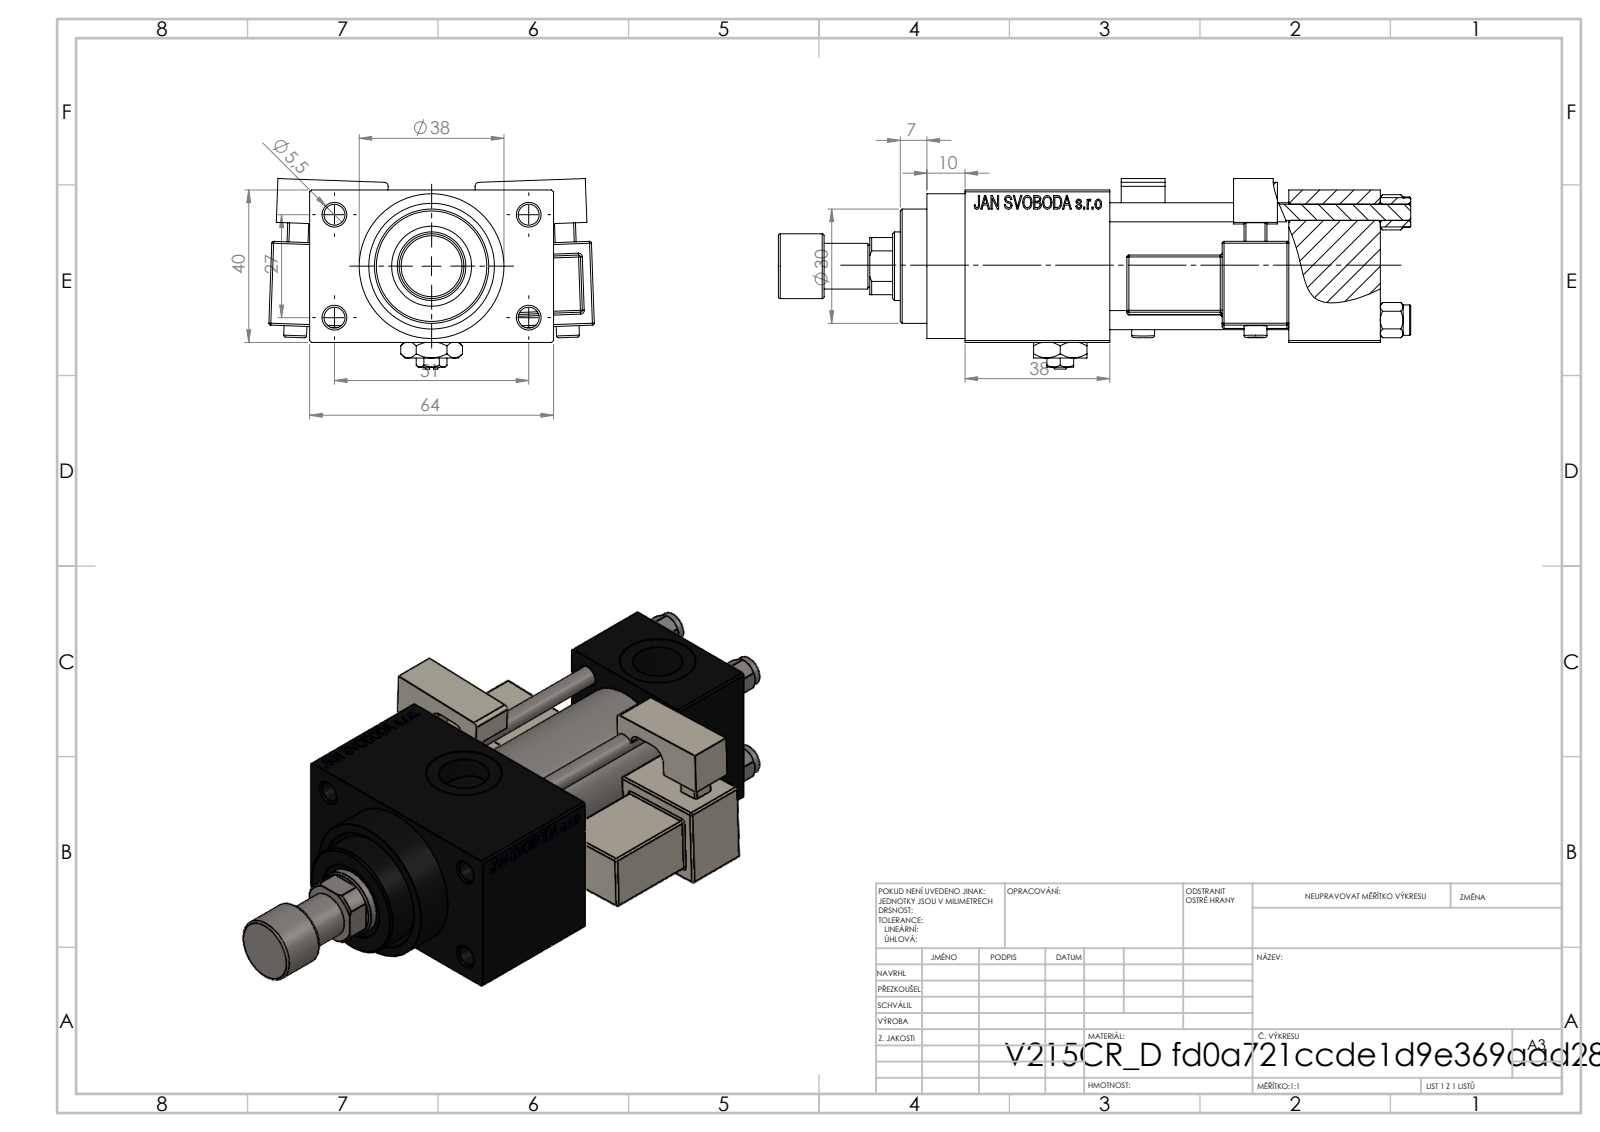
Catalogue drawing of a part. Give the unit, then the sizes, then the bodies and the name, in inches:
Units: inches
Overall size (bounding box): 6.535 × 3.362 × 1.968
Round holes (diameter × count): ⌀0.197 ×4, ⌀0.217 ×4, ⌀0.787 ×3, ⌀0.276 ×2, ⌀0.518 ×2, ⌀0.335 ×1, ⌀0.709 ×1, ⌀0.827 ×1, ⌀0.984 ×1, ⌀1.181 ×1
Round bosses / shafts (diameter × count): ⌀0.315 ×4, ⌀0.236 ×2, ⌀1.496 ×1, ⌀1.22 ×1, ⌀0.669 ×1, ⌀0.472 ×1, ⌀0.433 ×1
Partial cylindrical surfaces — rounded edges, fillets, slot ends (radius × count): R0.02 ×48, R0.039 ×2, R0.098 ×2, R0.157 ×2
Main face-to-face distances: 1.575, 1.85, 0.472, 0.945, 2.047, 1.496, 0.118, 0.787, 2.795, 2.52
Hole centre spacings: 0.448, 0.788, 1.114, 1.136, 1.177, 1.561, 1.903, 1.063
Volume: 13.75 in³ · Surface area: 121.2 in²
Bodies: 15 solids, 1321 faces (584 planar, 157 cylindrical, 580 other)
Part name (STEP PRODUCT): V215CR_VCP_D; V215_VC_A; V215CR_D_TYCINKA; V215CR_ROD_END_F (+4 more)
STEP written by: SolidWorks 2019 (CONFIG_CONTROL_DESIGN)
